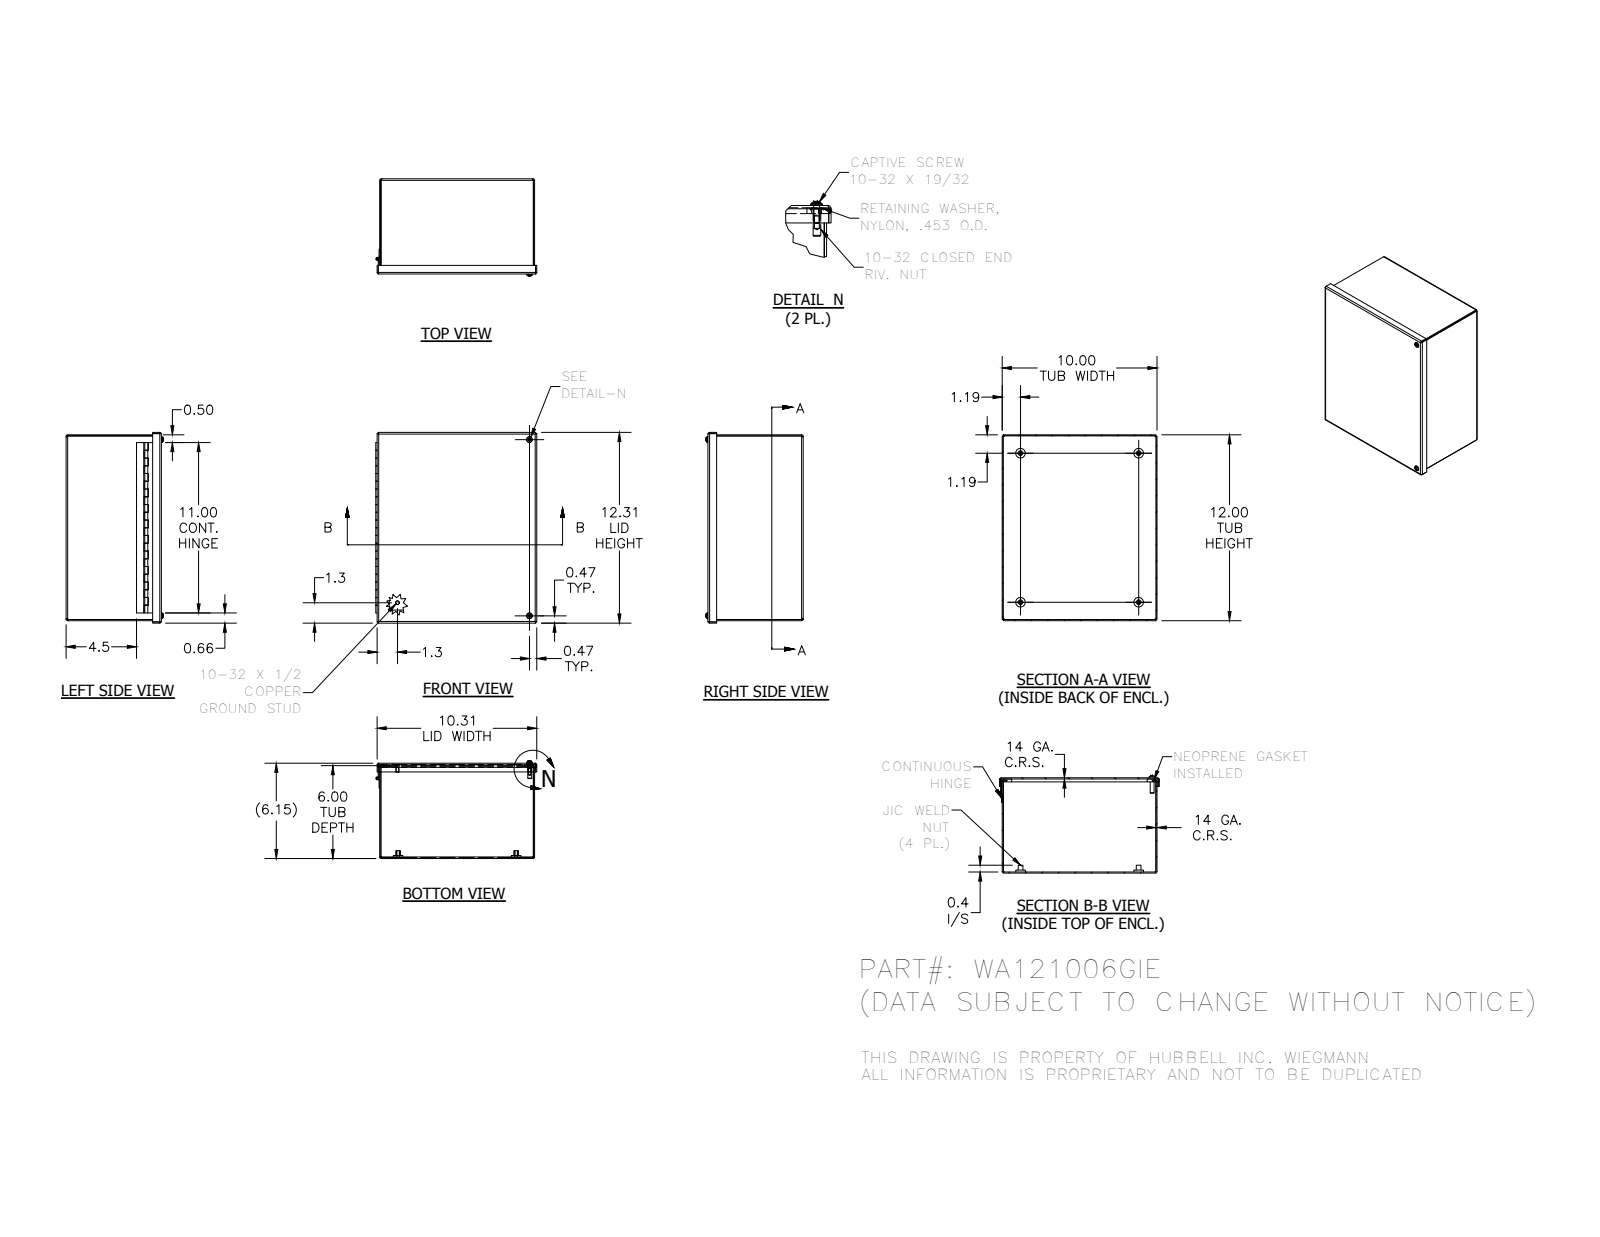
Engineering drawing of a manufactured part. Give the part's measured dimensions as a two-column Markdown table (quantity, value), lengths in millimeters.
| quantity | value |
| --- | --- |
| part name | WA121006GIEBKP; 3499; 328123LH; 328123P (+8 more) |
| STEP written by | Autodesk Inventor 2014 (AUTOMOTIVE_DESIGN) |
| units | millimeters |
| bodies | 18 solids, 485 faces (281 planar, 129 cylindrical, 75 other) |
| overall size | 312.74 × 264.08 × 159.56 |
| volume | 761 540 mm³ |
| surface area | 780 675 mm² |
| round holes (diameter × count) | 3.96 × 6, 6.53 × 4, 7.94 × 4, 4.98 × 2, 7.06 × 2, 7.14 × 2, 2.96 × 1 |
| round bosses / shafts (diameter × count) | 15.88 × 4, 7.62 × 4, 4.83 × 3, 11.51 × 2, 10.31 × 2, 9.47 × 2, 6.3 × 2, 6.35 × 1 |
| partial cylindrical surfaces (radius × count) | 0.79 × 12, 2.67 × 12, 1.78 × 8, 2.27 × 2 |
| main face-to-face distances | 1.88, 154.38, 252.12, 152.5, 156.26, 302.92, 254, 250.24, 304.8, 301.04 |
| hole center spacings | 288.92, 31.42, 217.04, 238.12, 288.91, 238.41, 267.62, 343.14 |
